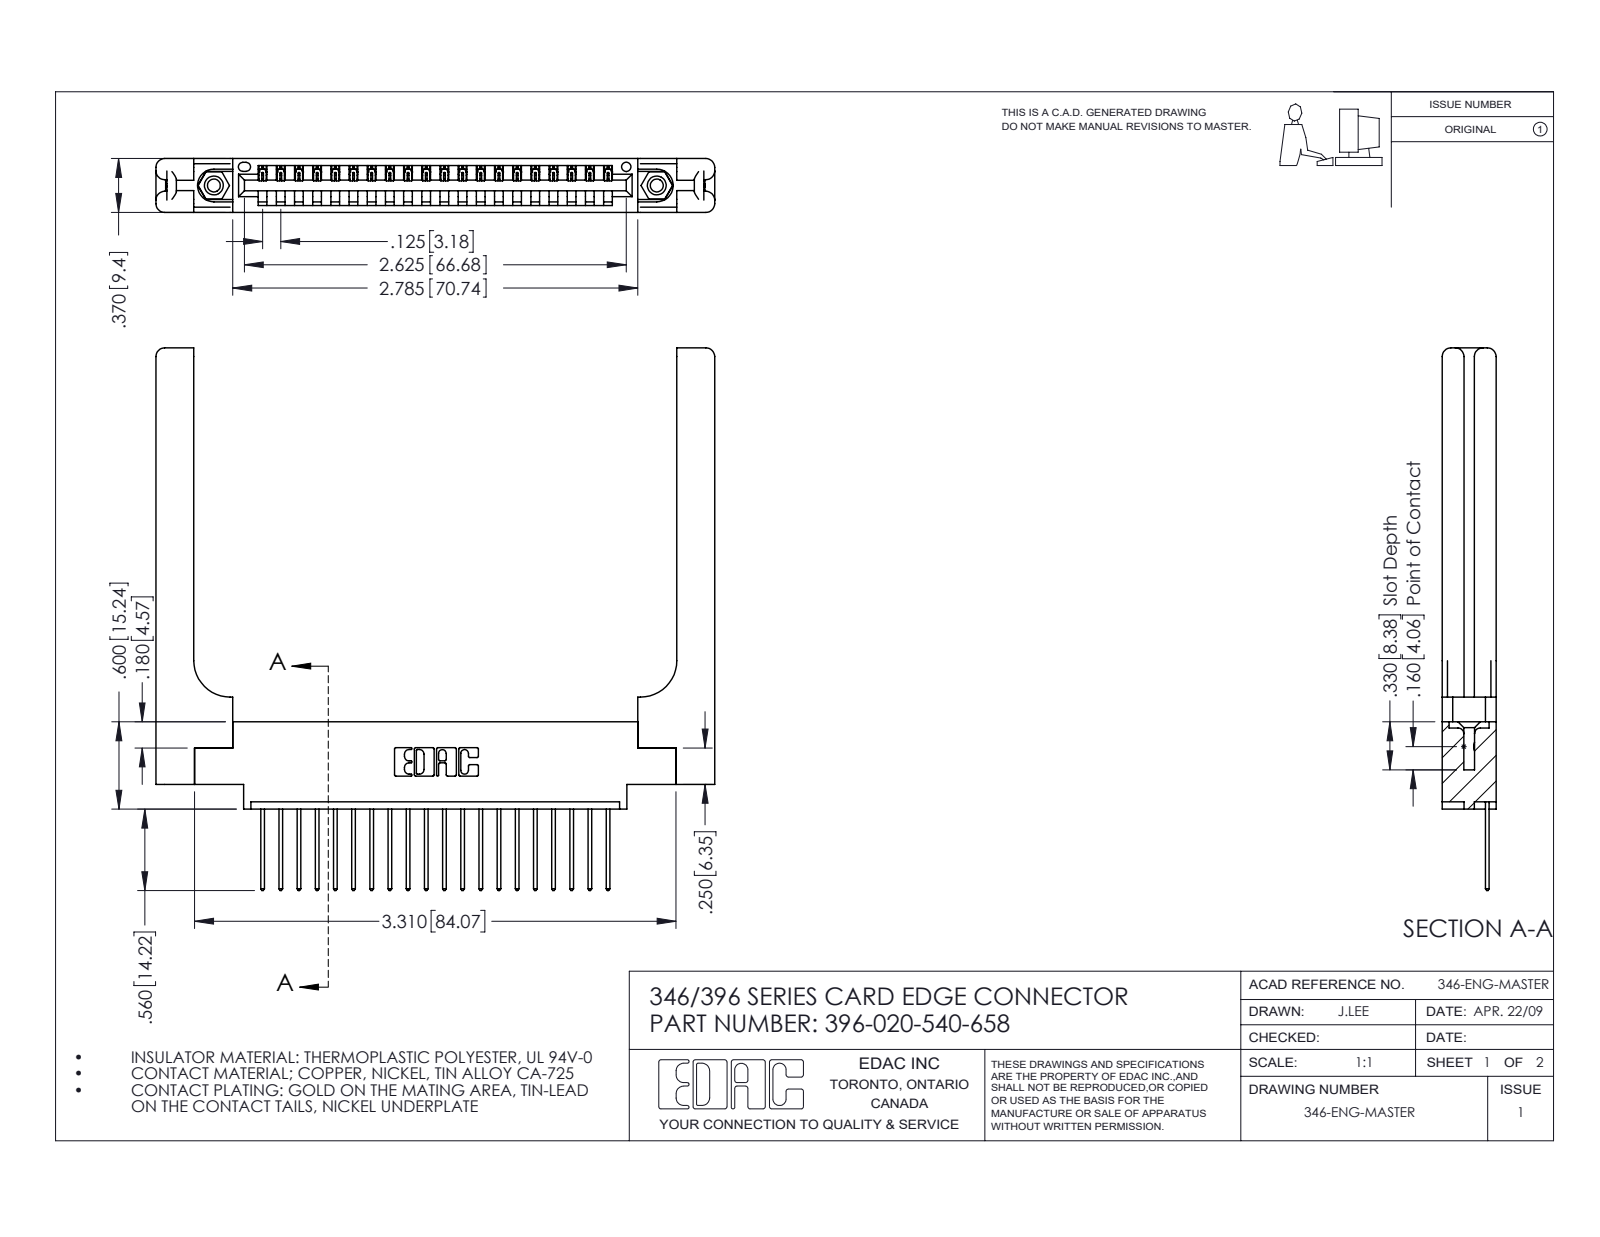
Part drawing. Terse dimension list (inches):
name: 345-250-001_345-250-001-102; 346 Part_0.170 Offset - 0.156 Dia-TH; 345-292-001_345-293-140; 396-020-540-658 (+1 more)
written by: SolidWorks 2016 (CONFIG_CONTROL_DESIGN)
unit: in
bodies: 25 solids, 1542 faces (1028 planar, 454 cylindrical, 60 other)
size: 3.841 × 3.73 × 0.37
volume: 1.012 in³; area: 25.75 in²
holes: 2× ⌀0.089, 2× ⌀0.125, 2× ⌀0.156, 1× ⌀0.064
bosses: 2× ⌀0.155
rounds: 40× R0.006, 40× R0.01, 22× R0.01, 16× R0.06, 6× R0.007, 6× R0.031, 3× R0.026, 2× R0.03
face distances: 0.37, 0.072, 0.048, 0.322, 0.15, 0.148, 0.25, 0.298, 0.025, 0.102
hole spacings: 0.246, 2.837, 3.045
